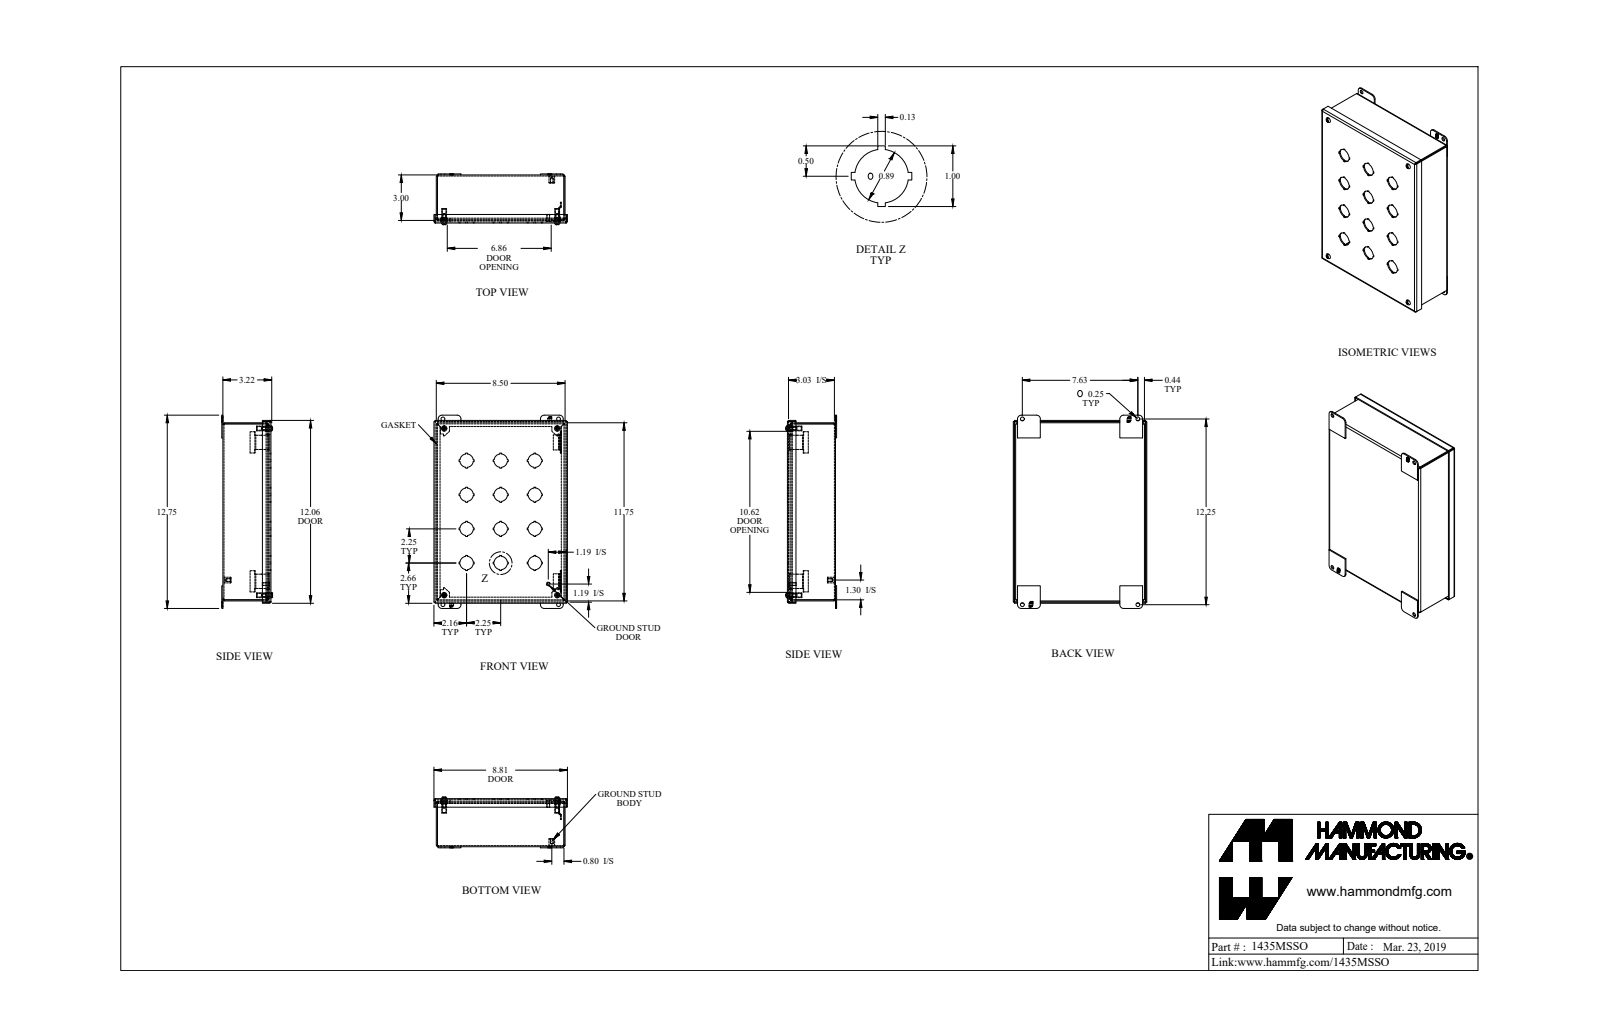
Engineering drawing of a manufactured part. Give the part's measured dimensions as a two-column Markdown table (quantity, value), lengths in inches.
| quantity | value |
| --- | --- |
| part name | 1435MSSO_Default |
| STEP written by | SolidWorks 2019 (CONFIG_CONTROL_DESIGN) |
| units | inches |
| bodies | 23 solids, 797 faces (567 planar, 200 cylindrical, 30 other) |
| overall size | 12.75 × 8.81 × 3.354 |
| volume | 29.39 in³ |
| surface area | 780.7 in² |
| round holes (diameter × count) | 0.886 × 12, 0.25 × 8, 0.065 × 4, 0.239 × 4, 0.253 × 4, 0.406 × 4, 0.156 × 1 |
| round bosses / shafts (diameter × count) | 0.19 × 5, 0.406 × 4, 0.315 × 4, 0.148 × 4, 0.375 × 1, 0.25 × 1 |
| partial cylindrical surfaces (radius × count) | 0.036 × 12, 0.108 × 12, 0.25 × 8, 0.029 × 4, 0.086 × 4, 0.171 × 4 |
| main face-to-face distances | 0.072, 3.1, 3.172, 3.028, 8.428, 0.072, 11.678, 8.5, 8.356, 0.155 |
| hole center spacings | 2.25, 5.031, 3.182, 4.5, 7.46, 7.461, 7.569, 10.999 |
